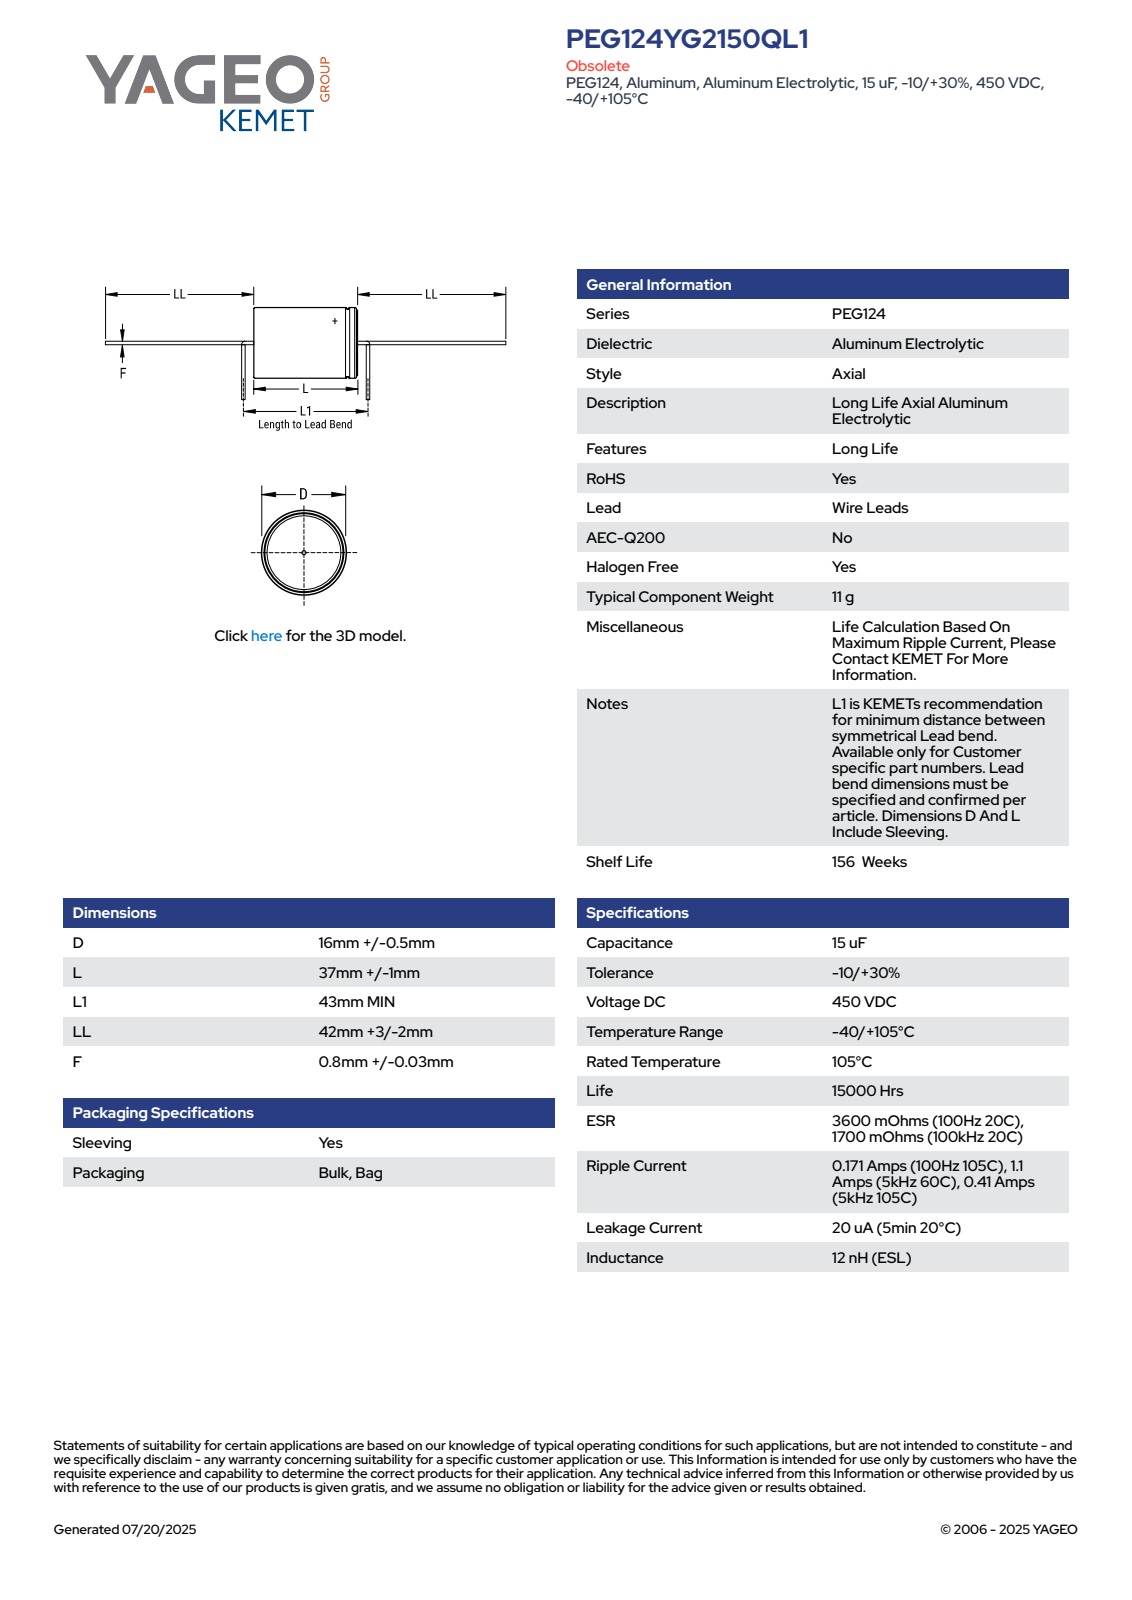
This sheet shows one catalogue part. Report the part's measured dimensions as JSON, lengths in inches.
{"part_name": "CAA_PEG124_16X37_D16.5L38LL45F0.83", "step_written_by": "SolidWorks 2014 (AUTOMOTIVE_DESIGN)", "units": "inches", "bodies": {"solids": 1, "faces": 99, "planar": 27, "cylindrical": 29, "other": 43}, "overall_size": [4.921, 0.65, 0.65], "volume_in3": 0.487, "surface_area_in2": 4.152, "round_holes": [[0.61, 1]], "round_bosses_or_shafts": [[0.65, 1], [0.63, 1], [0.033, 1]], "partial_cylinders_radius": [[0.324, 1]], "face_to_face_distances": [1.457, 1.496, 0.039, 1.772, 3.228, 3.268, 4.921, 3.15, 1.693, 1.654]}
